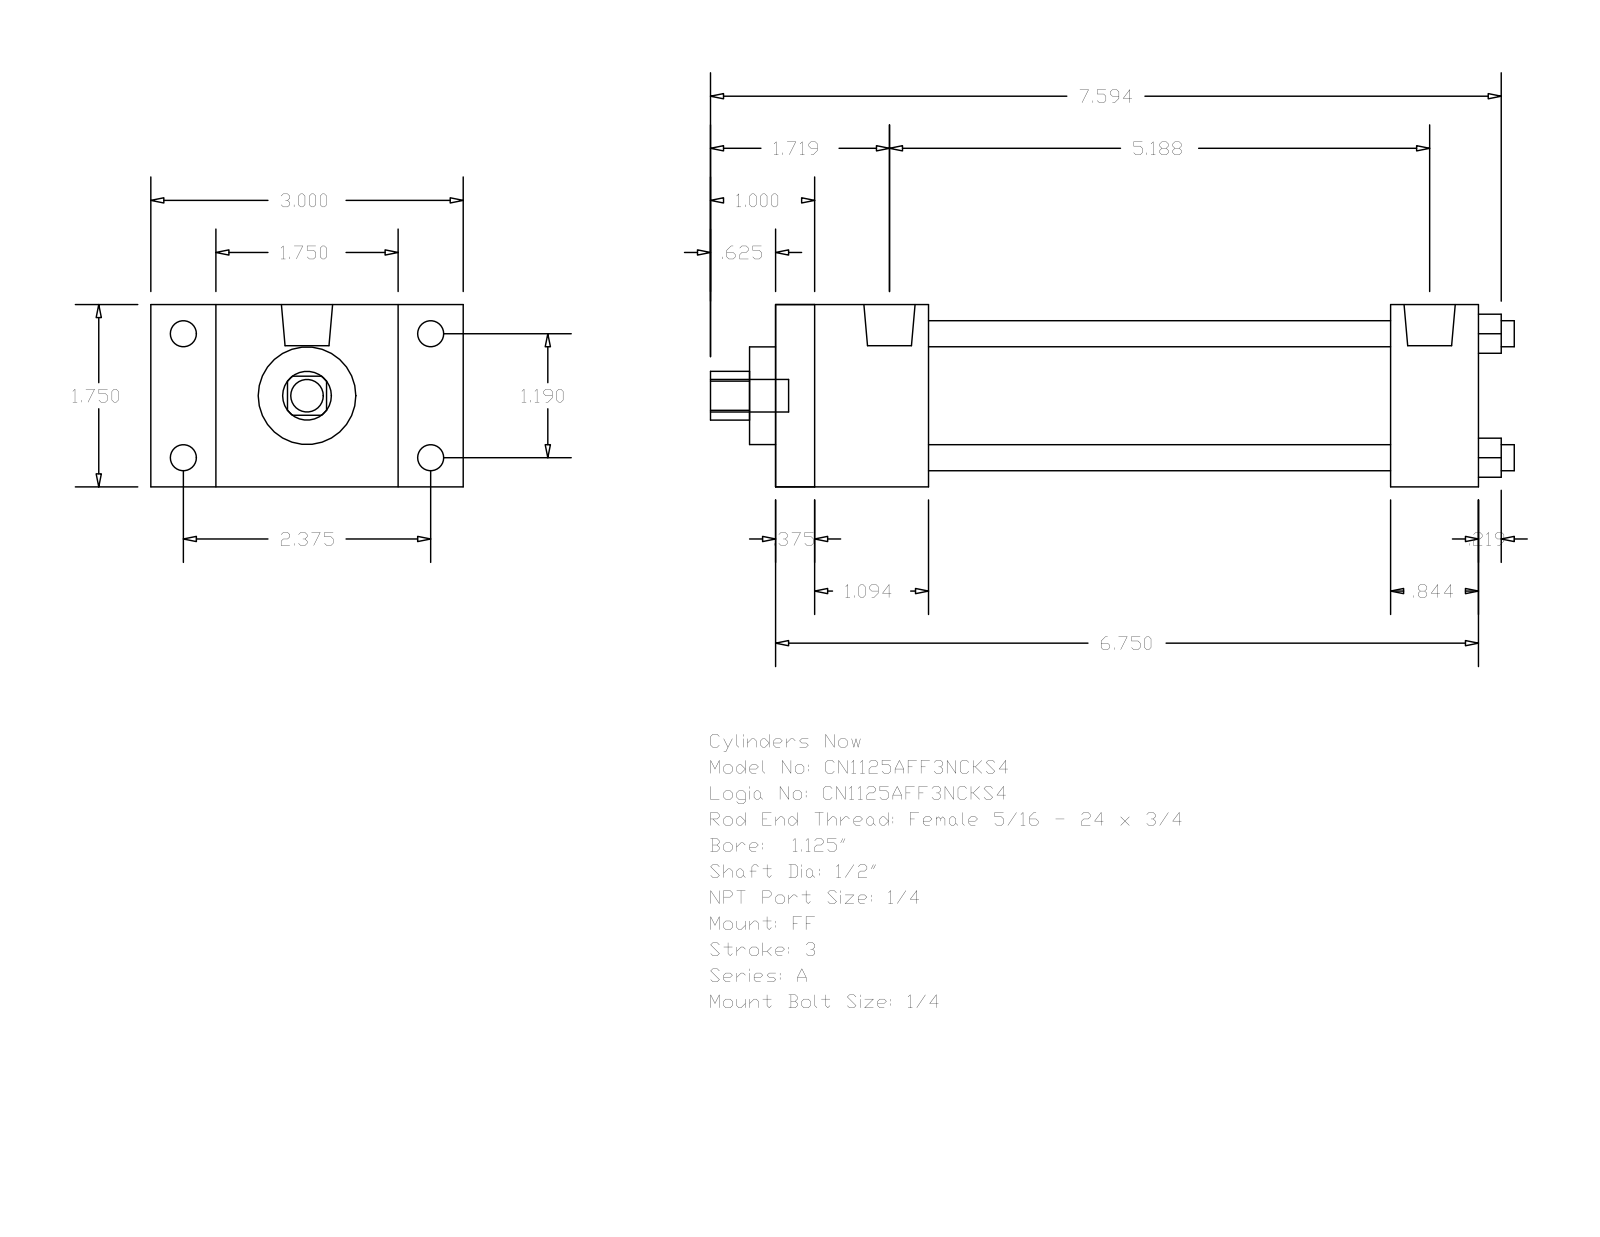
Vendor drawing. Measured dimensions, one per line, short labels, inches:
name: A_FF__0112_0.5
written by: GSSL Pune (CONFIG_CONTROL_DESIGN)
unit: in
bodies: 0 solids, 92 faces (64 planar, 28 cylindrical, 0 other)
size: 7.719 × 3 × 1.75
holes: 4× ⌀0.25, 1× ⌀0.5, 1× ⌀0.937, 1× ⌀1.255
bosses: 4× ⌀0.25, 4× ⌀0.219, 2× ⌀0.492, 1× ⌀0.313
rounds: 1× R0.234
face distances: 1.75, 6.75, 0.375, 6.375, 0.625, 5.906, 5.531, 0.844, 1.469, 1.094
hole spacings: 0.841, 1.19, 1.683
